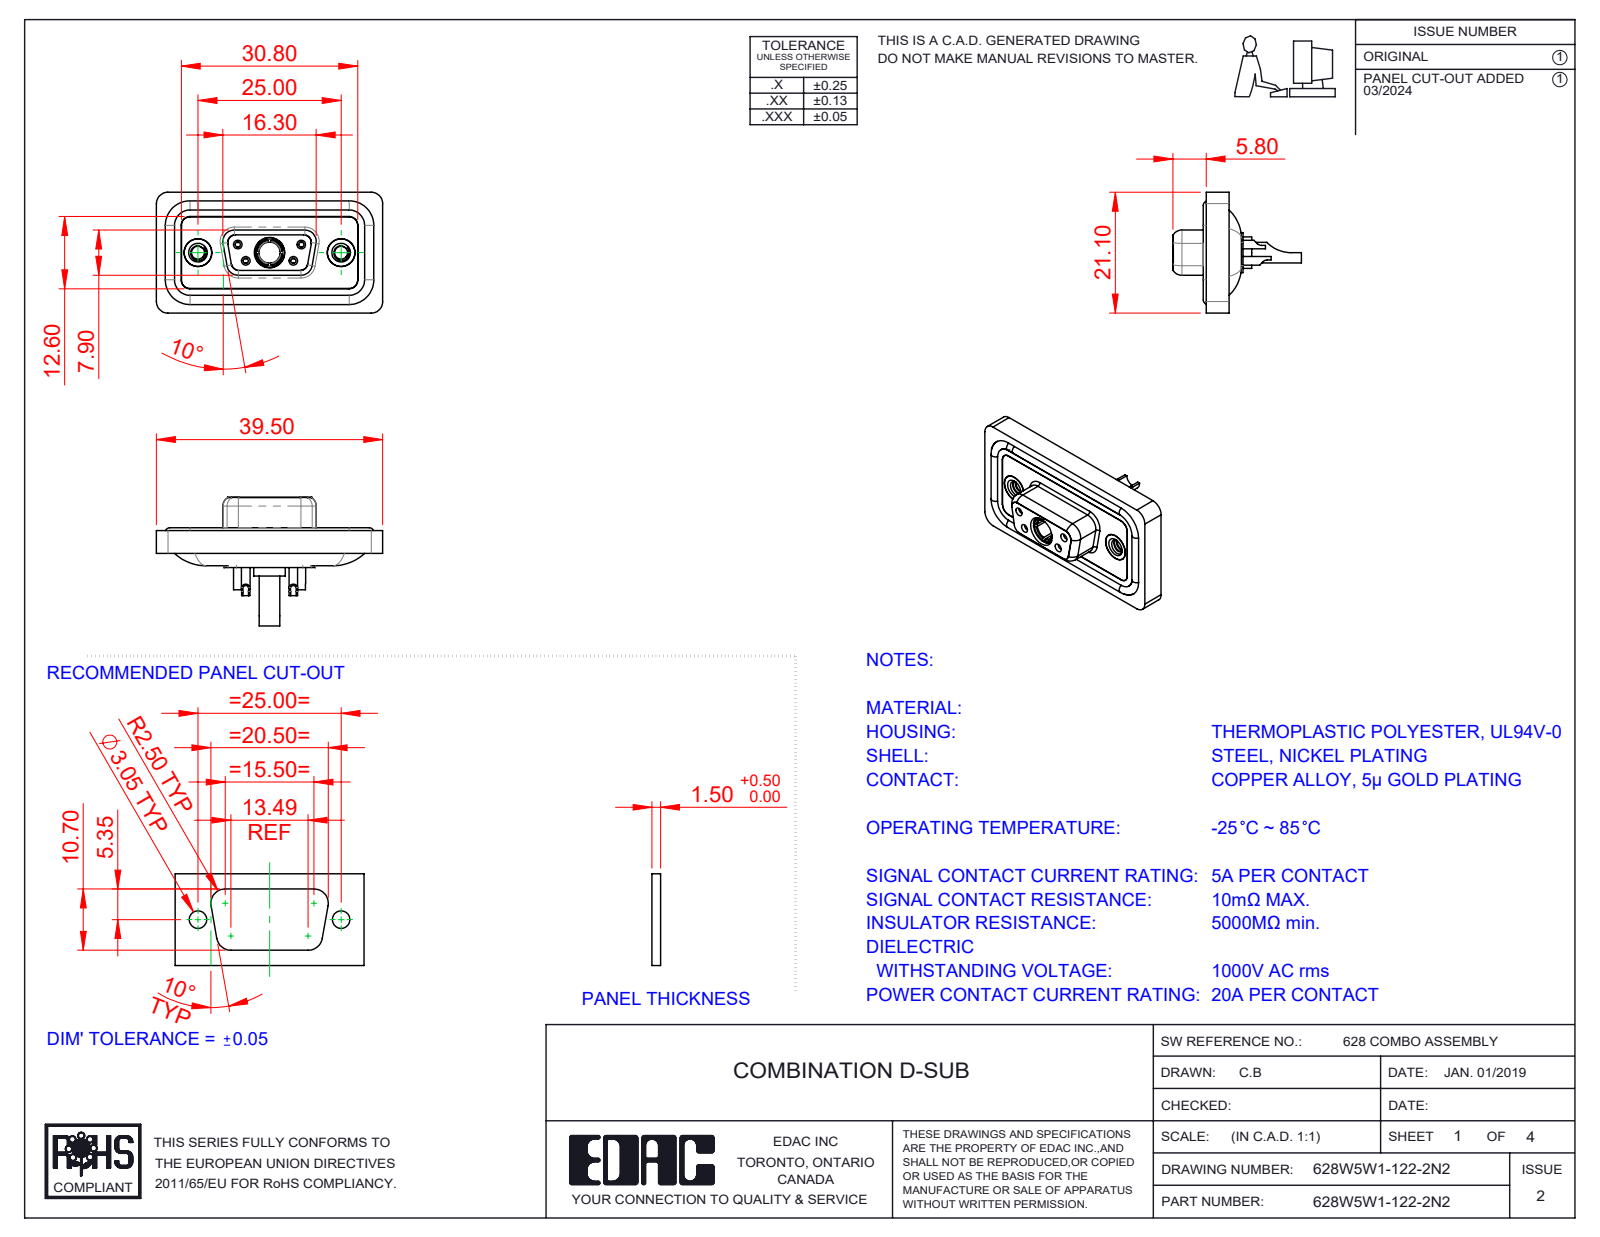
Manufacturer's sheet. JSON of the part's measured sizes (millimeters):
{"part_name": "628Combo Shell Front_09 Contacts; Power Socket_20A SC; 628Combo Waterproof Housing_09 Contacts; 628Combo Threaded Rivet_2 (+5 more)", "step_written_by": "SolidWorks 2023 (CONFIG_CONTROL_DESIGN)", "units": "millimeters", "bodies": {"solids": 13, "faces": 686, "planar": 205, "cylindrical": 298, "other": 183}, "overall_size": [39.5, 22.45, 21.1], "volume_mm3": 4788, "surface_area_mm2": 7760, "round_holes": [[0.9, 4], [1, 4], [1.1, 4], [1.5, 4], [2, 4], [4.85, 3], [1.6, 2], [1.7, 2], [2.26, 2], [4, 2], [4.05, 2], [5, 2]], "round_bosses_or_shafts": [[1.6, 6], [2.2, 4], [4.95, 2], [4.8, 2], [5.5, 1], [5.2, 1], [4.96, 1], [4.75, 1]], "partial_cylinders_radius": [[1.5, 22], [2, 18], [1.35, 8], [1.6, 8], [1, 6], [0.25, 4], [0.5, 4], [0.6, 4]], "face_to_face_distances": [0.4, 2.9, 1.1, 1.8, 1.6, 0.5, 5.65, 7.45, 5.35, 3.6], "hole_center_spacings": [3.16, 5.72, 7.1, 12.5, 18.1, 4.39, 4.4, 8.31]}
